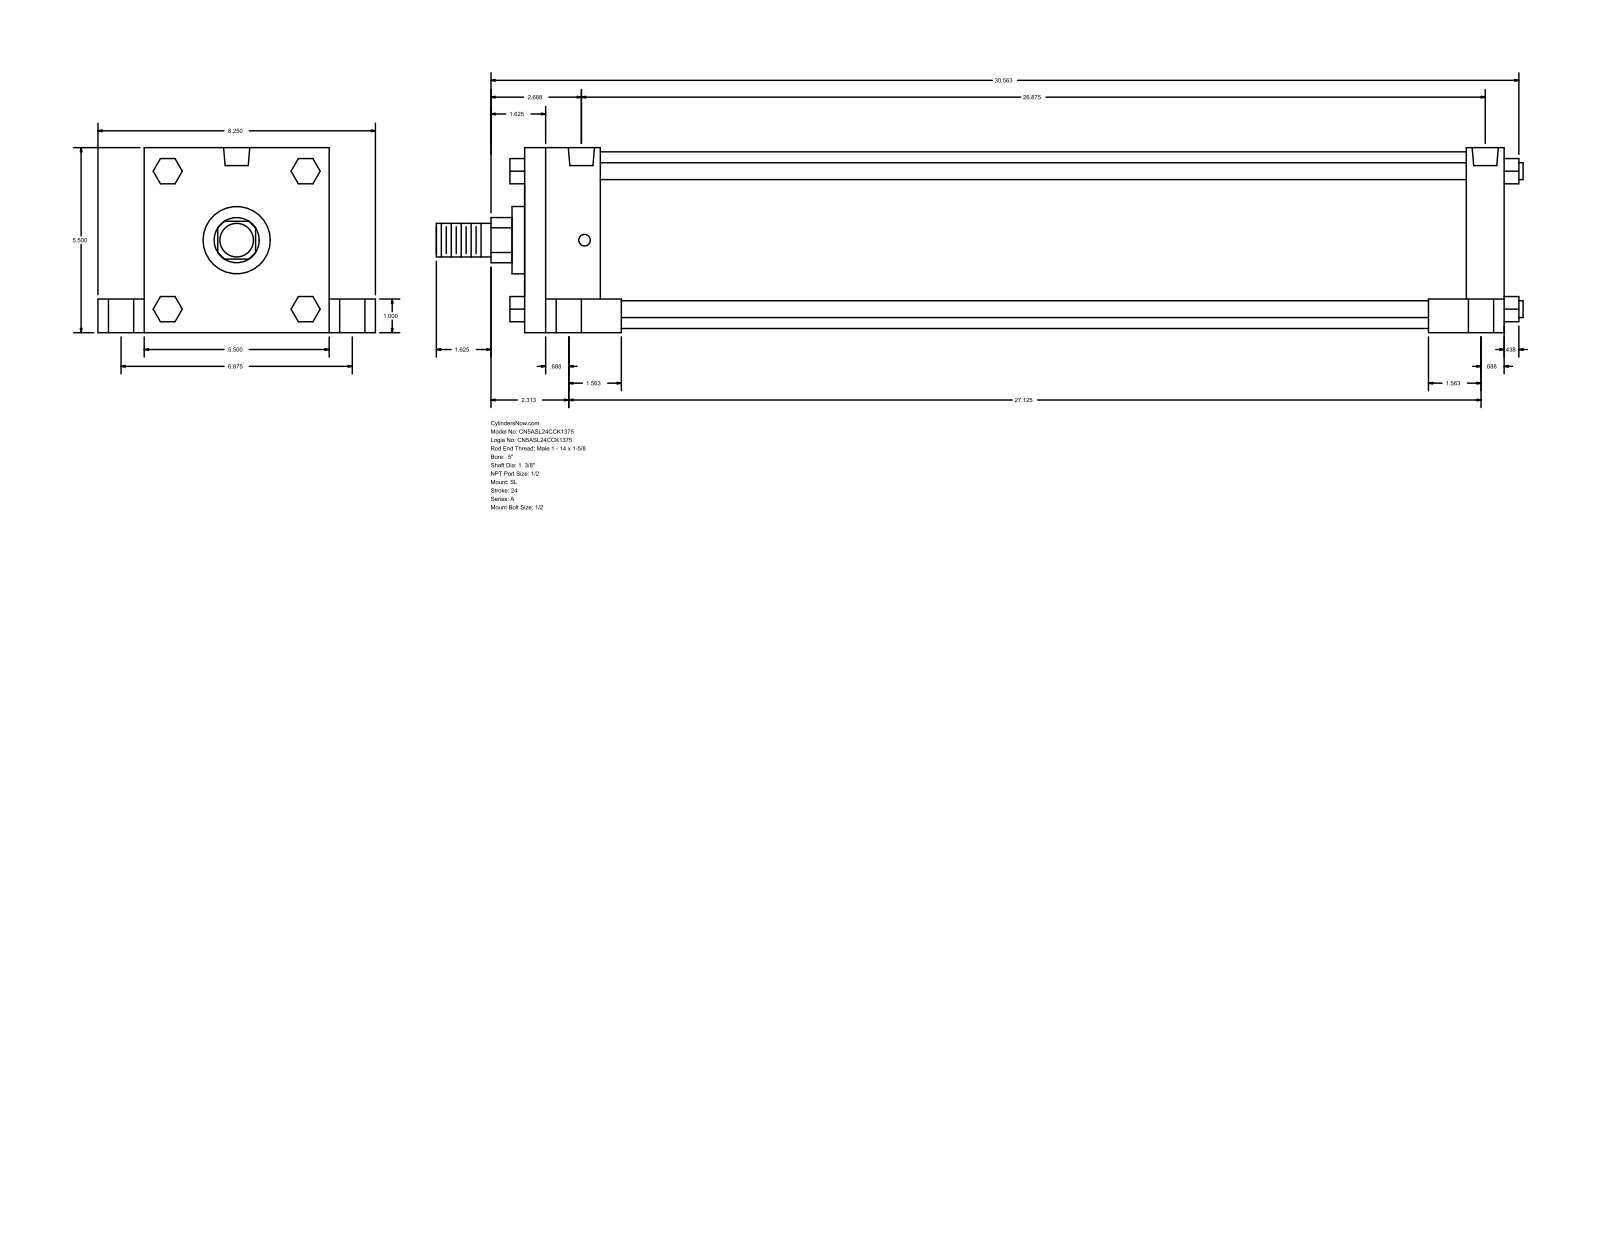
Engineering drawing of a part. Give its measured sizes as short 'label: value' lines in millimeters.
name: A_SL__0500_1.375
written by: GSSL Pune (CONFIG_CONTROL_DESIGN)
unit: mm
bodies: 0 solids, 150 faces (114 planar, 36 cylindrical, 0 other)
size: 820.74 × 209.55 × 139.7
holes: 4× ⌀8.73, 4× ⌀19.05, 4× ⌀25.4, 2× ⌀19.77
bosses: 4× ⌀12.7, 1× ⌀133.35, 1× ⌀50.8, 1× ⌀34.92, 1× ⌀25.4
rounds: 1× R17.06
face distances: 139.7, 739.77, 57.15, 682.62, 25.4, 114.3, 34.93, 174.63, 28.57, 711.2
hole spacings: 2.39, 87.31, 87.37, 87.83, 88.12, 174.62, 677.85, 680.24
